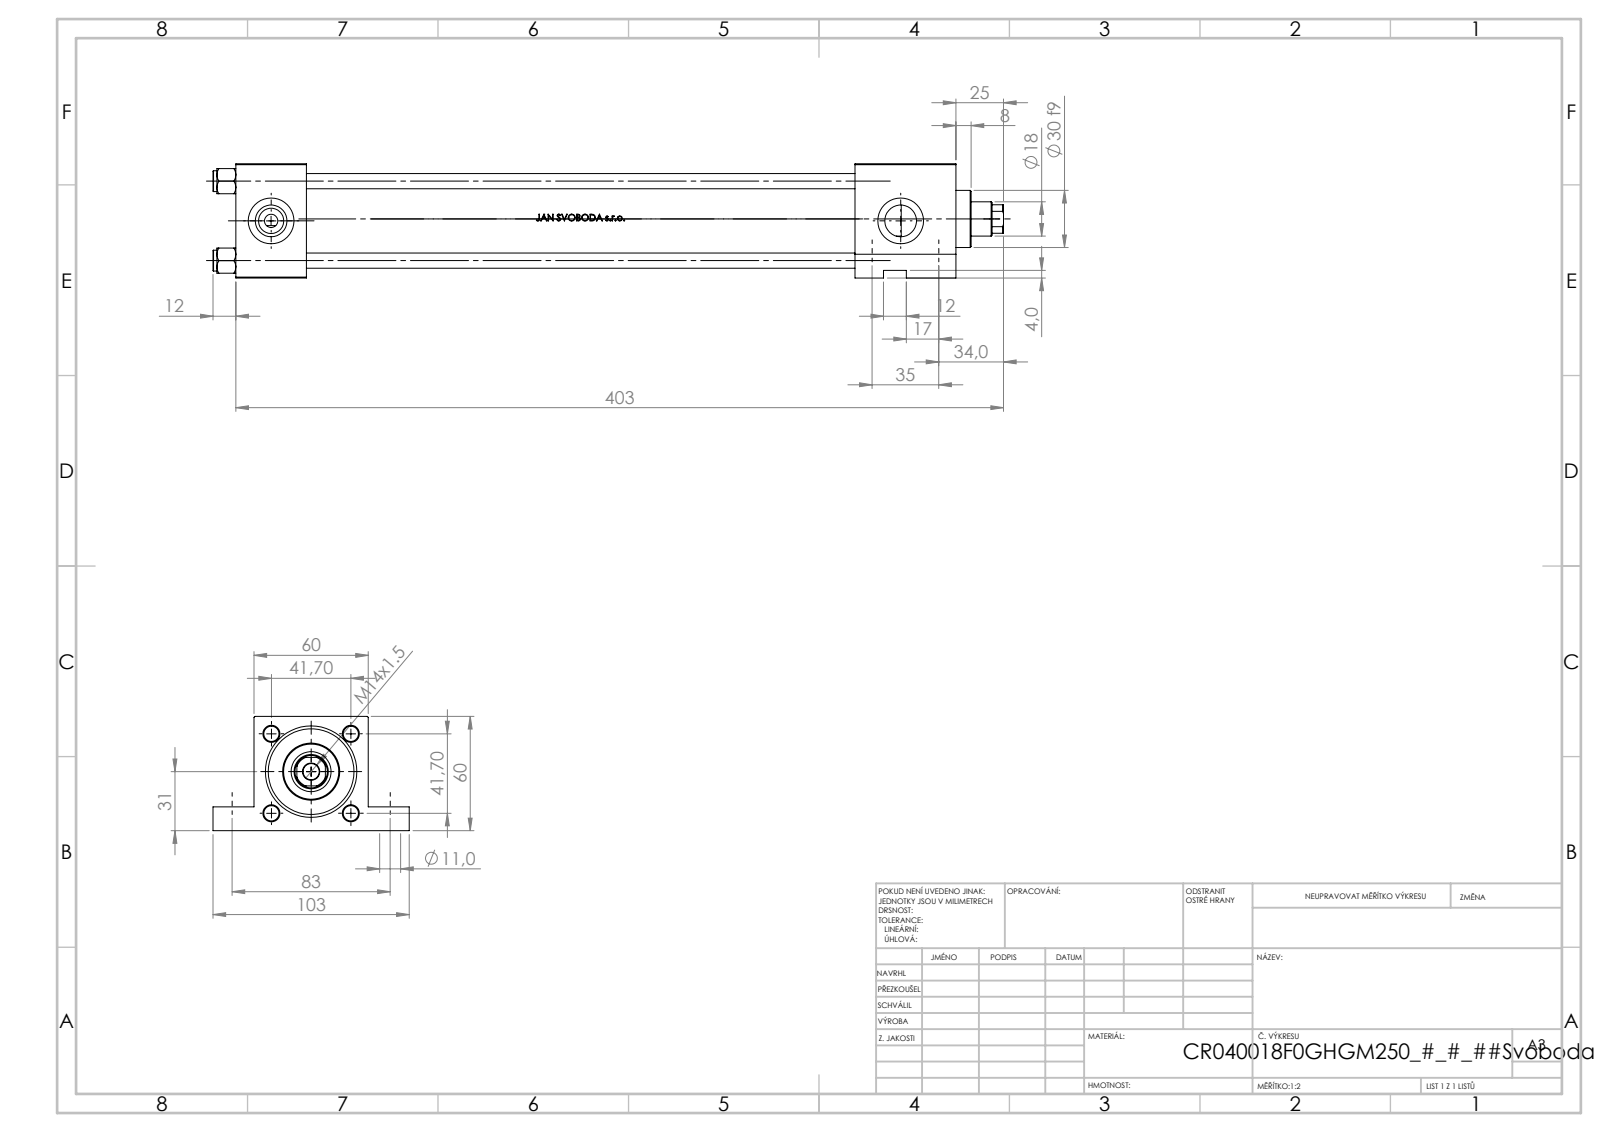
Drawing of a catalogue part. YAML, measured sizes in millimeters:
part_name: "NUT_M5_F; V215CR_F_Body; V215CR_VCP_F; V215CR_F_TYCINKA (+1 more)"
step_written_by: "SolidWorks 2019 (CONFIG_CONTROL_DESIGN)"
units: millimeters
bodies: {solids: 11, faces: 1118, planar: 437, cylindrical: 141, other: 540}
overall_size: [415, 103, 60]
volume: 621614
surface_area: 209806
round_holes:
  - {diameter: 8, count: 4}
  - {diameter: 11, count: 4}
  - {diameter: 7, count: 2}
  - {diameter: 16.66, count: 2}
  - {diameter: 24, count: 2}
  - {diameter: 8.5, count: 1}
  - {diameter: 18, count: 1}
  - {diameter: 21, count: 1}
  - {diameter: 31, count: 1}
  - {diameter: 40, count: 1}
  - {diameter: 45, count: 1}
round_bosses_or_shafts:
  - {diameter: 11, count: 4}
  - {diameter: 46, count: 1}
  - {diameter: 30, count: 1}
partial_cylinders:
  - {radius: 8.5, count: 1}
face_to_face_distances: [60, 37, 378, 341, 325, 288, 53, 349.3, 312.3, 24.3]
hole_center_spacings: [41.7, 28.79, 30.2, 35, 58.97, 83, 90.08, 330.5]
